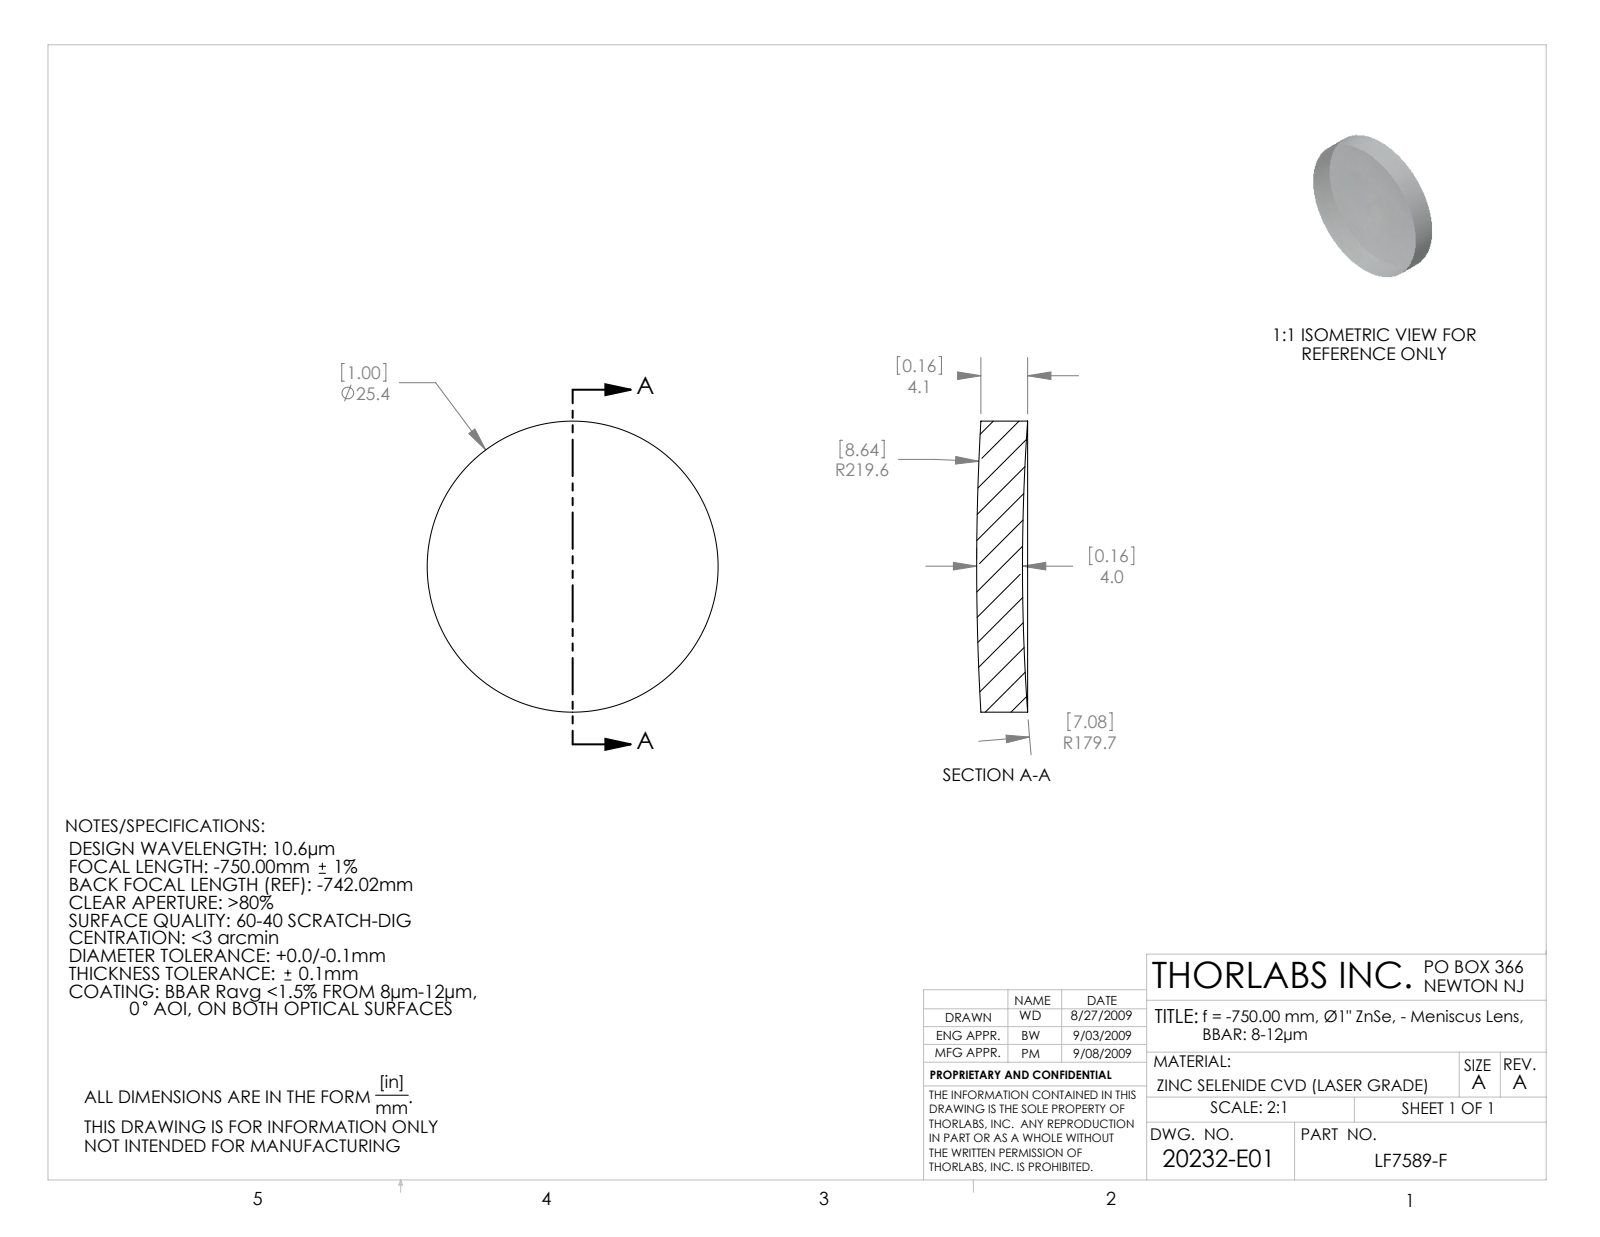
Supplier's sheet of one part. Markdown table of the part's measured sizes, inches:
| quantity | value |
| --- | --- |
| part name | 20232-E0W |
| STEP written by | SolidWorks 2007 (CONFIG_CONTROL_DESIGN) |
| units | inches |
| bodies | 1 solid, 6 faces (0 planar, 2 cylindrical, 4 other) |
| overall size | 1 × 1 × 0.175 |
| volume | 0.125 in³ |
| surface area | 2.077 in² |
| round bosses / shafts (diameter × count) | 1 × 1 |
